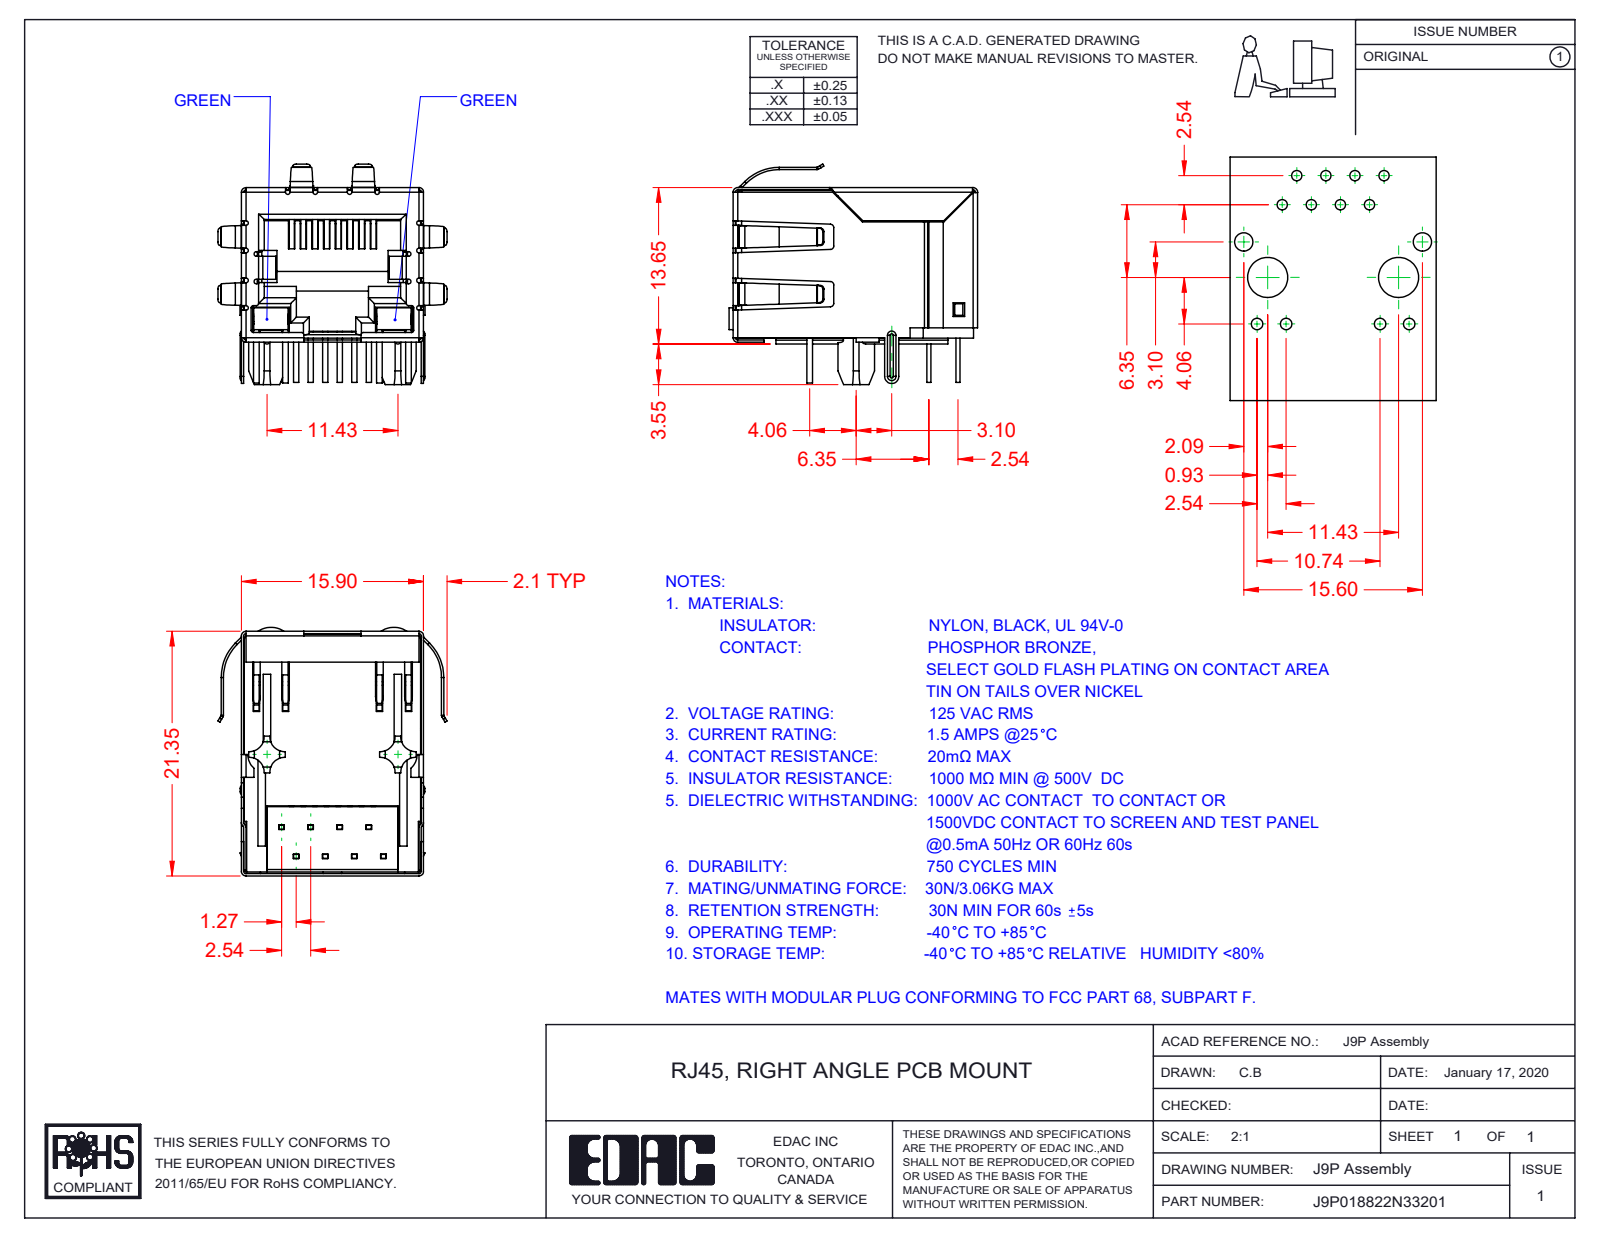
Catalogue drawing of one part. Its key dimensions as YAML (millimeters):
part_name: "9P-LED Contacts; 9P-LED Contact Lock; 9P-LED Shield; J9P018822N33202 (+4 more)"
step_written_by: "SolidWorks 2016 (CONFIG_CONTROL_DESIGN)"
units: millimeters
bodies: {solids: 13, faces: 1472, planar: 1042, cylindrical: 336, other: 94}
overall_size: [21.7, 20, 19.25]
volume: 2687
surface_area: 7515
partial_cylinders:
  - {radius: 0.2, count: 39}
  - {radius: 0.5, count: 22}
  - {radius: 0.3, count: 20}
  - {radius: 0.4, count: 16}
  - {radius: 1.3, count: 8}
  - {radius: 0.23, count: 5}
  - {radius: 0.11, count: 4}
  - {radius: 0.31, count: 4}
face_to_face_distances: [15.45, 15.7, 15.65, 0.35, 0.54, 15.5, 12.36, 0.6, 1.4, 0.59]
